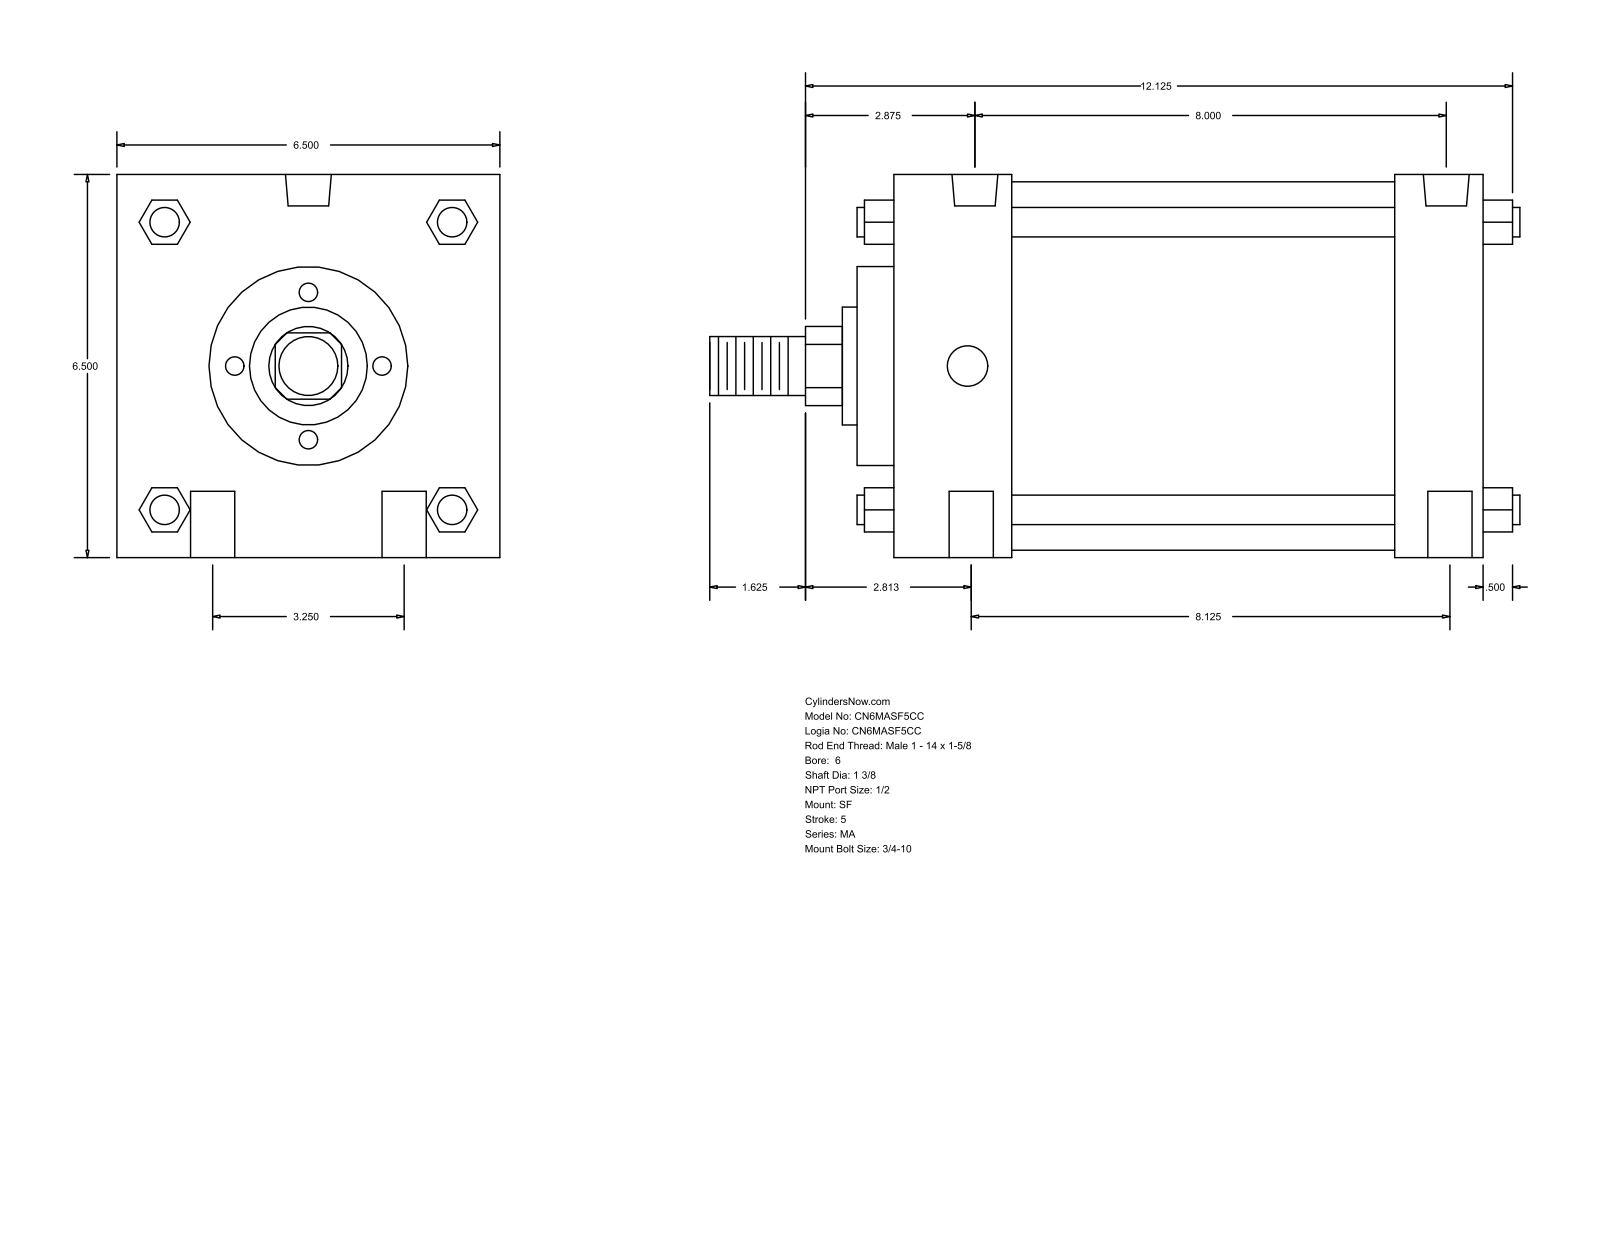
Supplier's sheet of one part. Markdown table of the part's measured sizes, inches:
| quantity | value |
| --- | --- |
| part name | MA_SF__0600_1.375 |
| STEP written by | GSSL Pune (CONFIG_CONTROL_DESIGN) |
| units | inches |
| bodies | 0 solids, 126 faces (95 planar, 31 cylindrical, 0 other) |
| overall size | 13.75 × 6.5 × 6.5 |
| round holes (diameter × count) | 0.75 × 4, 0.687 × 2, 0.778 × 2 |
| round bosses / shafts (diameter × count) | 0.5 × 4, 6.25 × 1, 3.375 × 1, 2 × 1, 1.375 × 1, 1 × 1 |
| partial cylindrical surfaces (radius × count) | 0.672 × 1 |
| main face-to-face distances | 6.5, 10, 8.5, 2, 1.5, 8, 2.625, 0.625, 9.125, 10.625 |
| hole center spacings | 1.626, 3.25, 8, 8.125, 8.224, 8.225, 8.75 |
